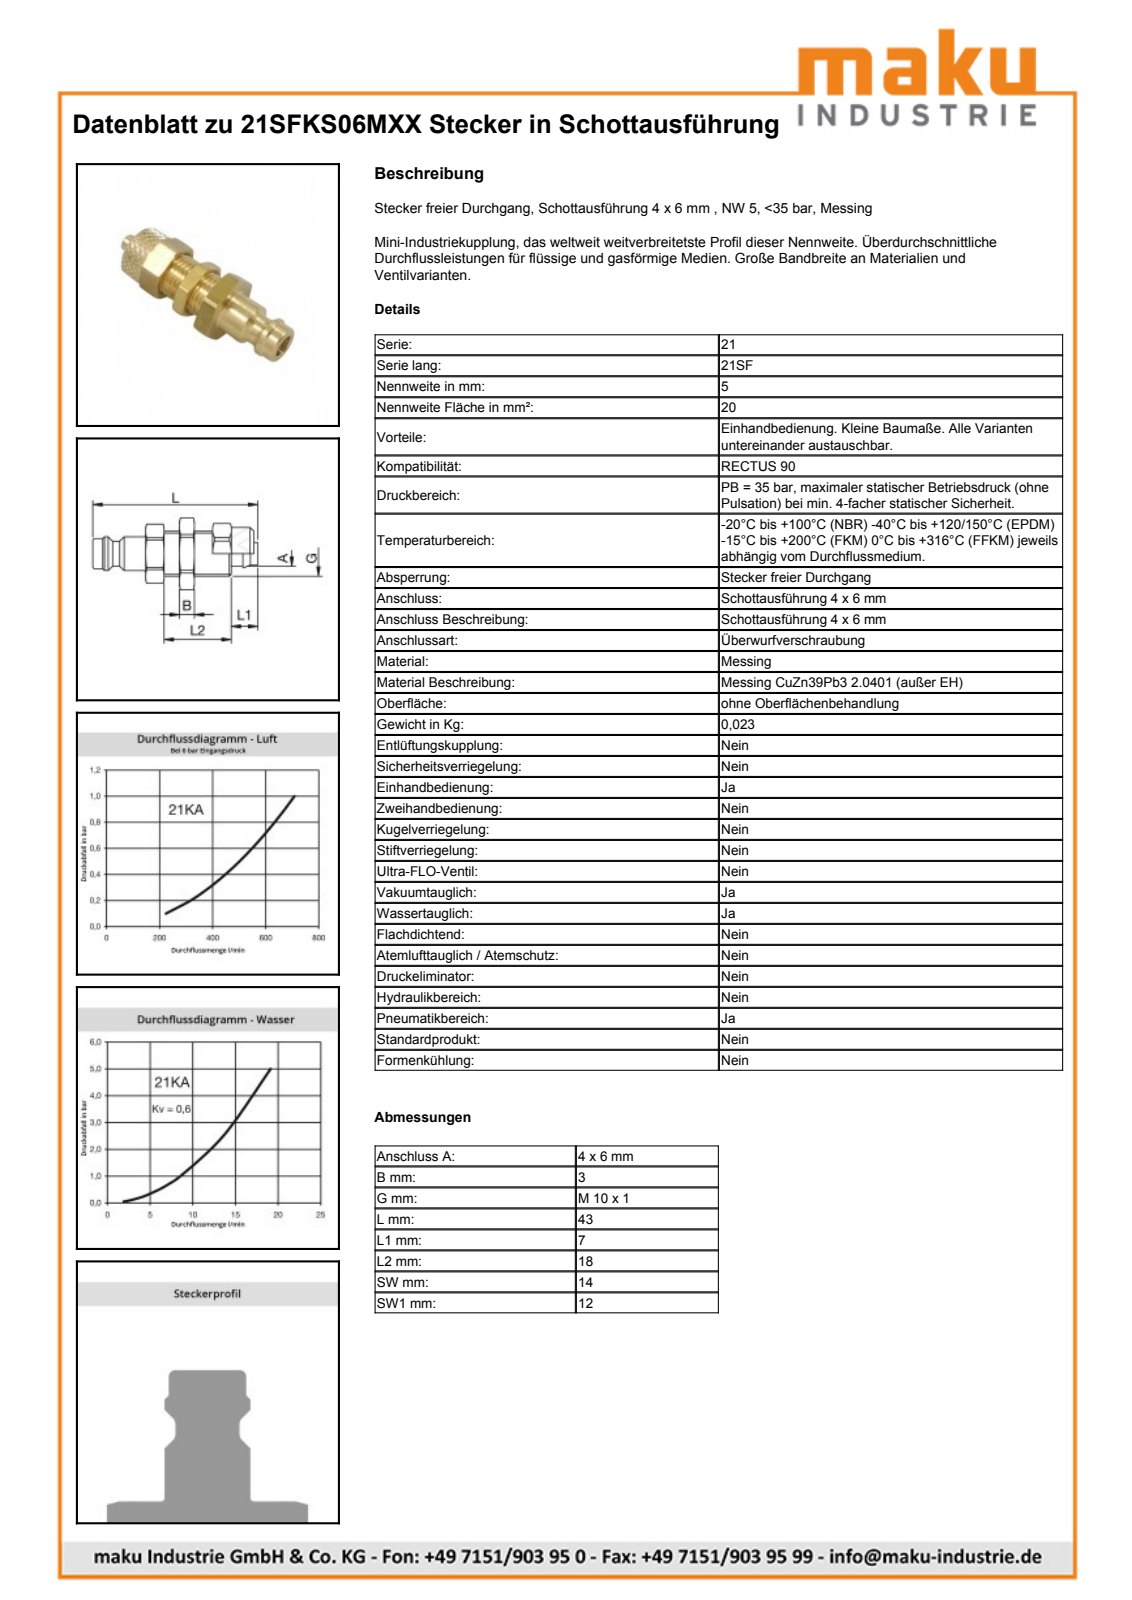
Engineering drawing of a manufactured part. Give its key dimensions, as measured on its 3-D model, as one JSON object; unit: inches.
{"part_name": "D108980; D108979; D108978; D102148", "step_written_by": "Autodesk Inventor 2013 (AUTOMOTIVE_DESIGN)", "units": "inches", "bodies": {"solids": 3, "faces": 109, "planar": 28, "cylindrical": 32, "other": 49}, "overall_size": [1.693, 0.622, 0.551], "volume_in3": 0.179, "surface_area_in2": 5.065, "round_holes": [[0.116, 1], [0.197, 1], [0.244, 1], [0.372, 1], [0.394, 1]], "round_bosses_or_shafts": [[0.472, 1], [0.354, 1], [0.339, 1], [0.319, 1], [0.262, 1], [0.181, 1], [0.156, 1]], "partial_cylinders_radius": [[0.266, 1], [0.311, 1]], "face_to_face_distances": [0.472, 0.551, 0.154, 1.107, 0.954, 0.858, 0.705, 0.249, 0.274, 0.392]}
